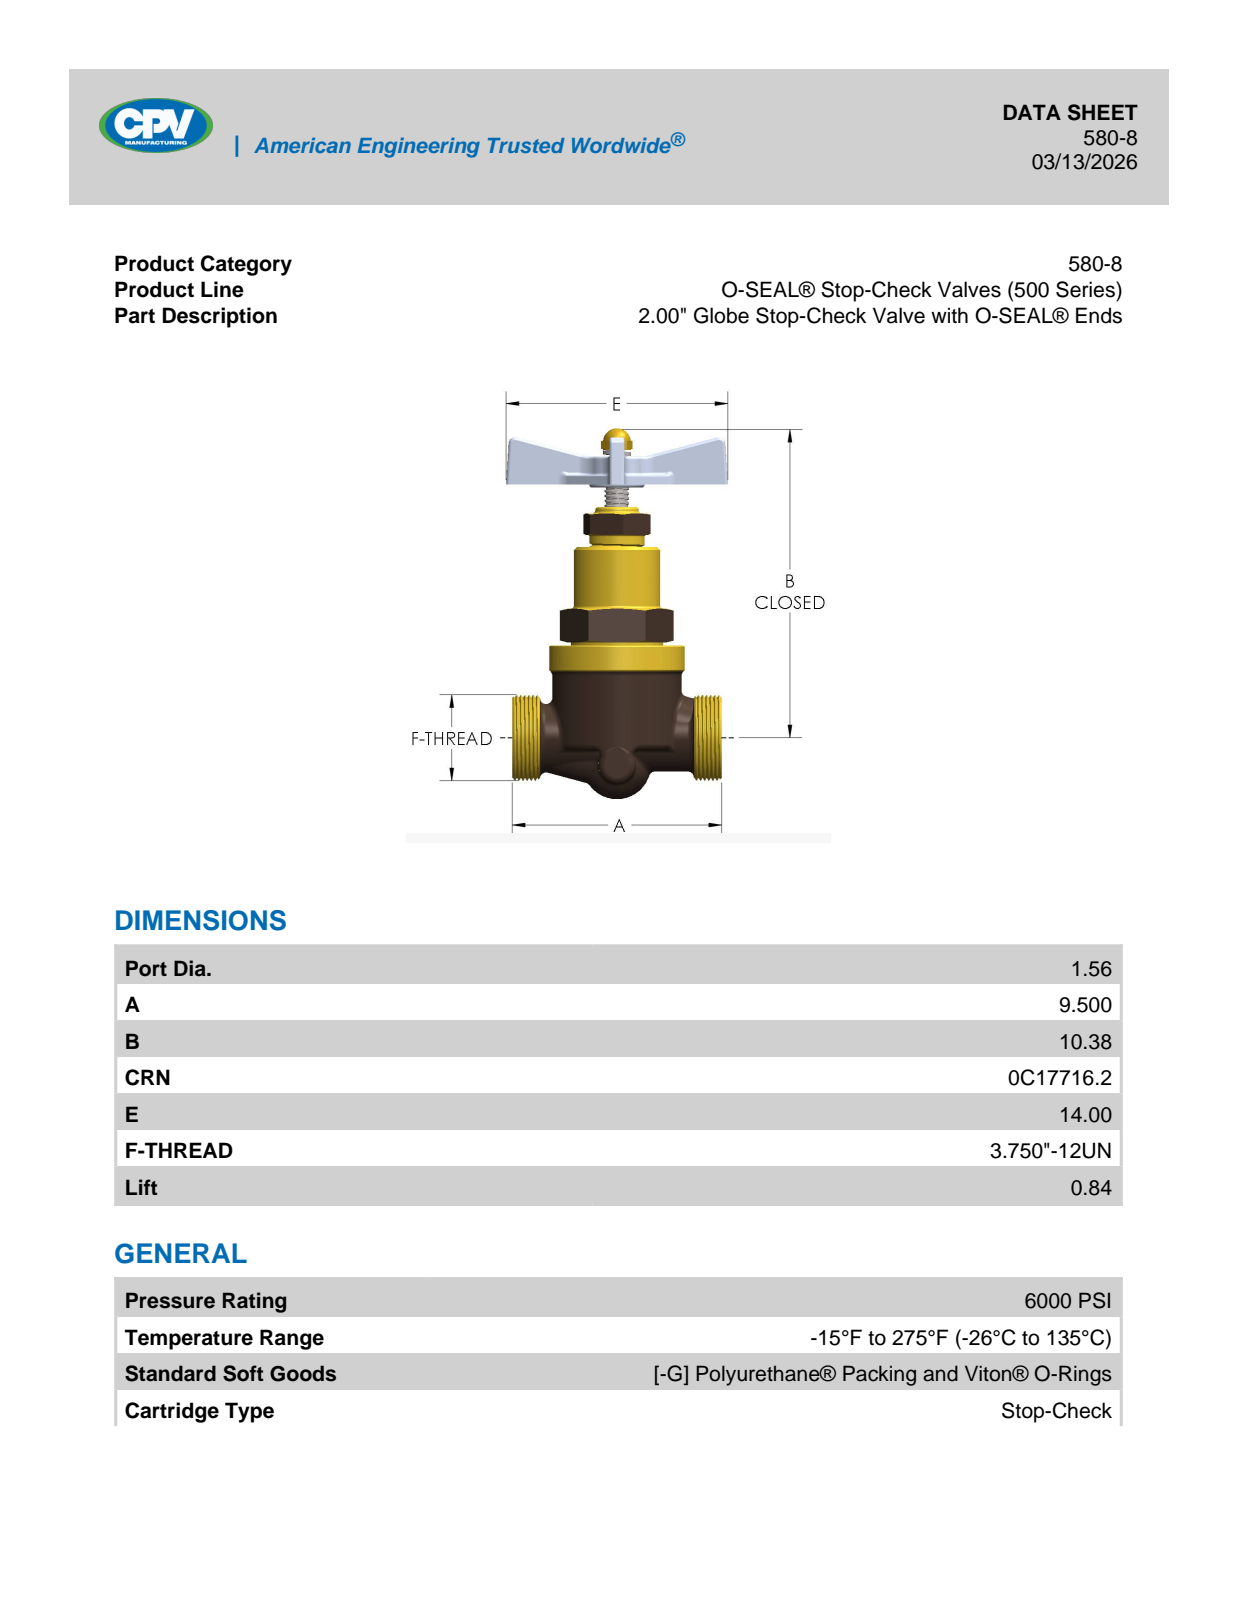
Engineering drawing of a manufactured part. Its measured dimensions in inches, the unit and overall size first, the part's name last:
Units: inches
Overall size (bounding box): 14 × 13.673 × 6.5
Round holes (diameter × count): ⌀1.563 ×3, ⌀0.509 ×1, ⌀1.91 ×1, ⌀3.66 ×1, ⌀4 ×1
Round bosses / shafts (diameter × count): ⌀3.75 ×2, ⌀6.5 ×1, ⌀6.25 ×1, ⌀3.873 ×1, ⌀3.635 ×1, ⌀3.625 ×1, ⌀3.438 ×1, ⌀3.25 ×1
Partial cylindrical surfaces — rounded edges, fillets, slot ends (radius × count): R0.13 ×14, R0.03 ×12, R0.625 ×2, R0.433 ×1, R1.227 ×1, R1.769 ×1, R3.245 ×1
Main face-to-face distances: 0.63, 4, 3.678, 9.6, 0.202, 3.88, 0.25, 8.788, 0.812, 6.393
Hole centre spacings: 2.25
Volume: 239.2 in³ · Surface area: 528.9 in²
Bodies: 1 solid, 635 faces (121 planar, 279 cylindrical, 235 other)
Part name (STEP PRODUCT): 380-8
STEP written by: SolidWorks 2018 (AUTOMOTIVE_DESIGN)
